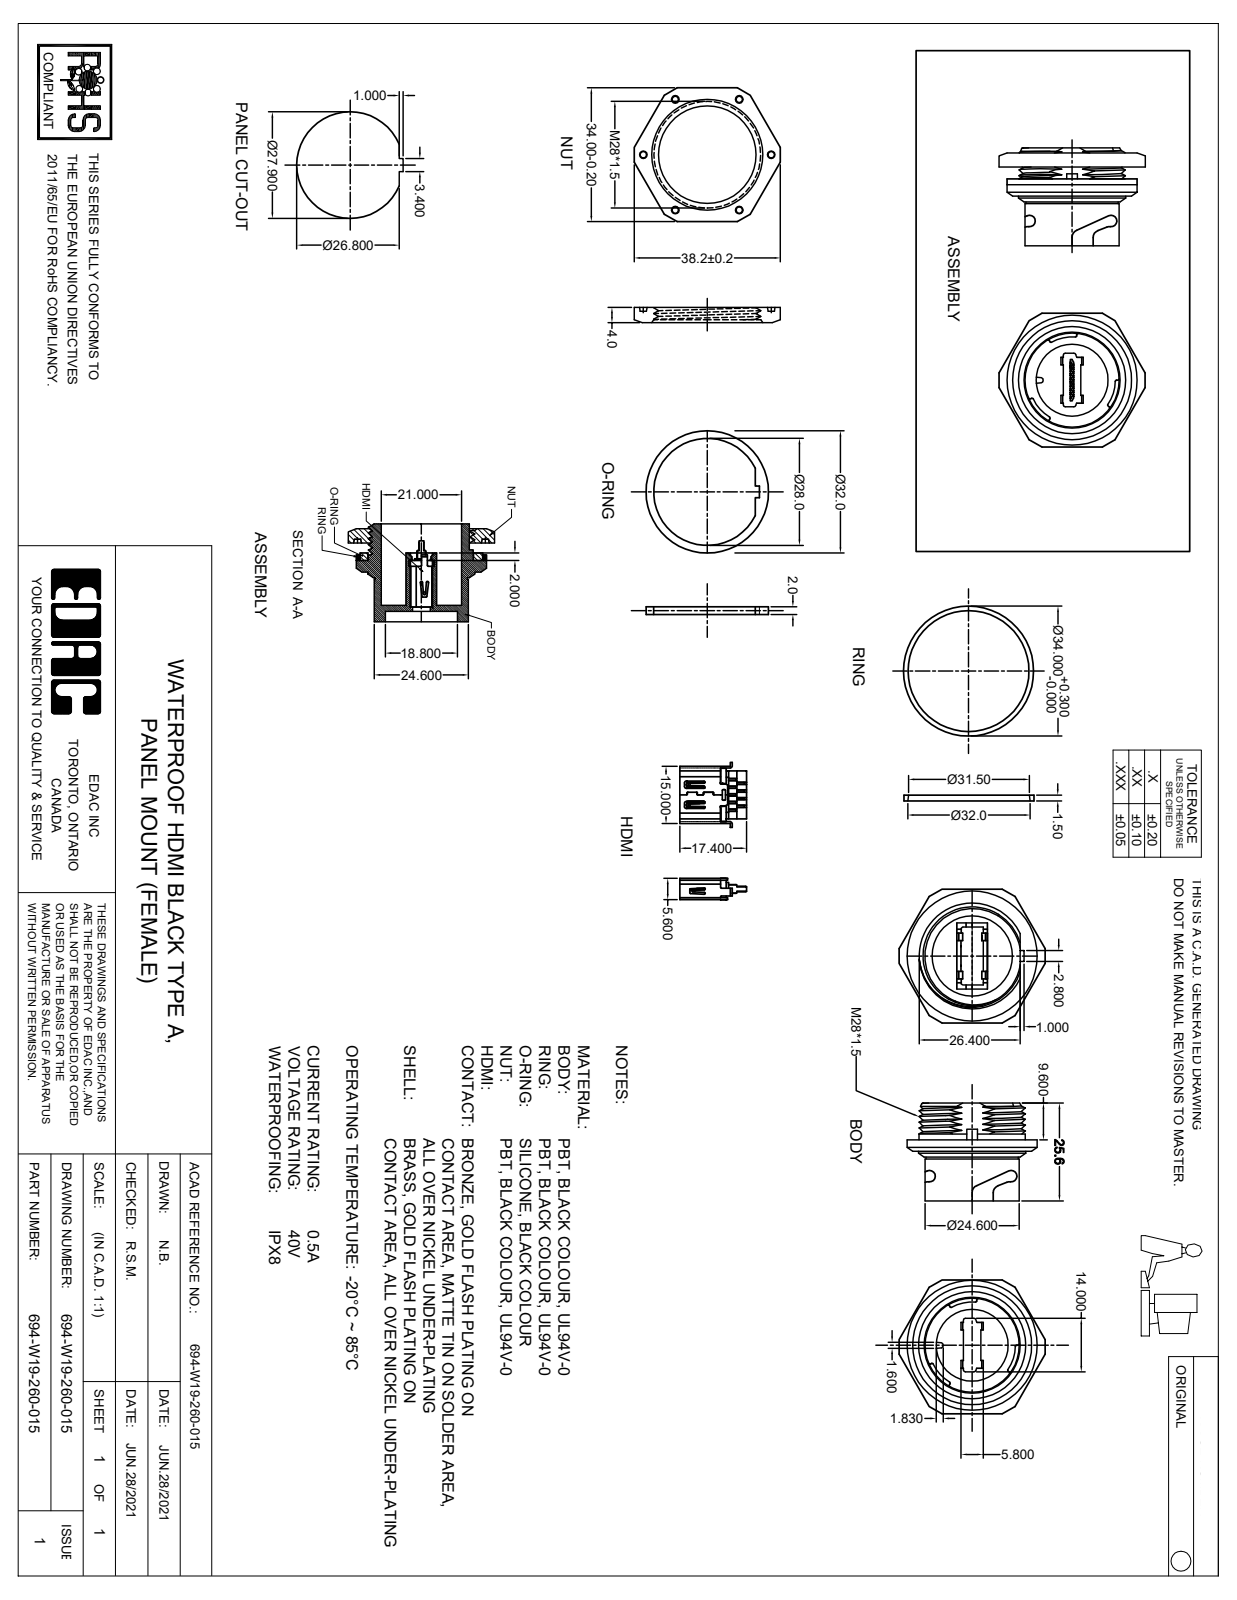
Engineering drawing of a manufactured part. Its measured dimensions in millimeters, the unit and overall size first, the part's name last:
Units: millimetres
Overall size (bounding box): 38.2 × 34.77 × 25.6
Round holes (diameter × count): ⌀2 ×6, ⌀18.8 ×1, ⌀21 ×1, ⌀26.25 ×1, ⌀28 ×1
Round bosses / shafts (diameter × count): ⌀34 ×1, ⌀32 ×1, ⌀27.8 ×1, ⌀24.6 ×1, ⌀24.1 ×1
Partial cylindrical surfaces — rounded edges, fillets, slot ends (radius × count): R0.15 ×240, R0.21 ×38, R0.2 ×28, R0.5 ×12, R0.25 ×10, R0.1 ×6, R0.35 ×6, R0.65 ×6
Main face-to-face distances: 0.5, 4, 4.93, 1.1, 2.7, 8.93, 2, 6.93, 9.6, 5.68
Hole centre spacings: 16.5, 28.58, 33, 16.51, 33.01
Volume: 9 559 mm³ · Surface area: 12 980 mm²
Bodies: 26 solids, 2027 faces (1388 planar, 574 cylindrical, 65 other)
Part name (STEP PRODUCT): O-RING 694-W19-X60-015; HDMI HOUSING2 694-W19-X60-015; 694-W19-260-015; HOUSING 694-W19-X60-015 (+7 more)
STEP written by: SolidWorks 2020 (AUTOMOTIVE_DESIGN)
